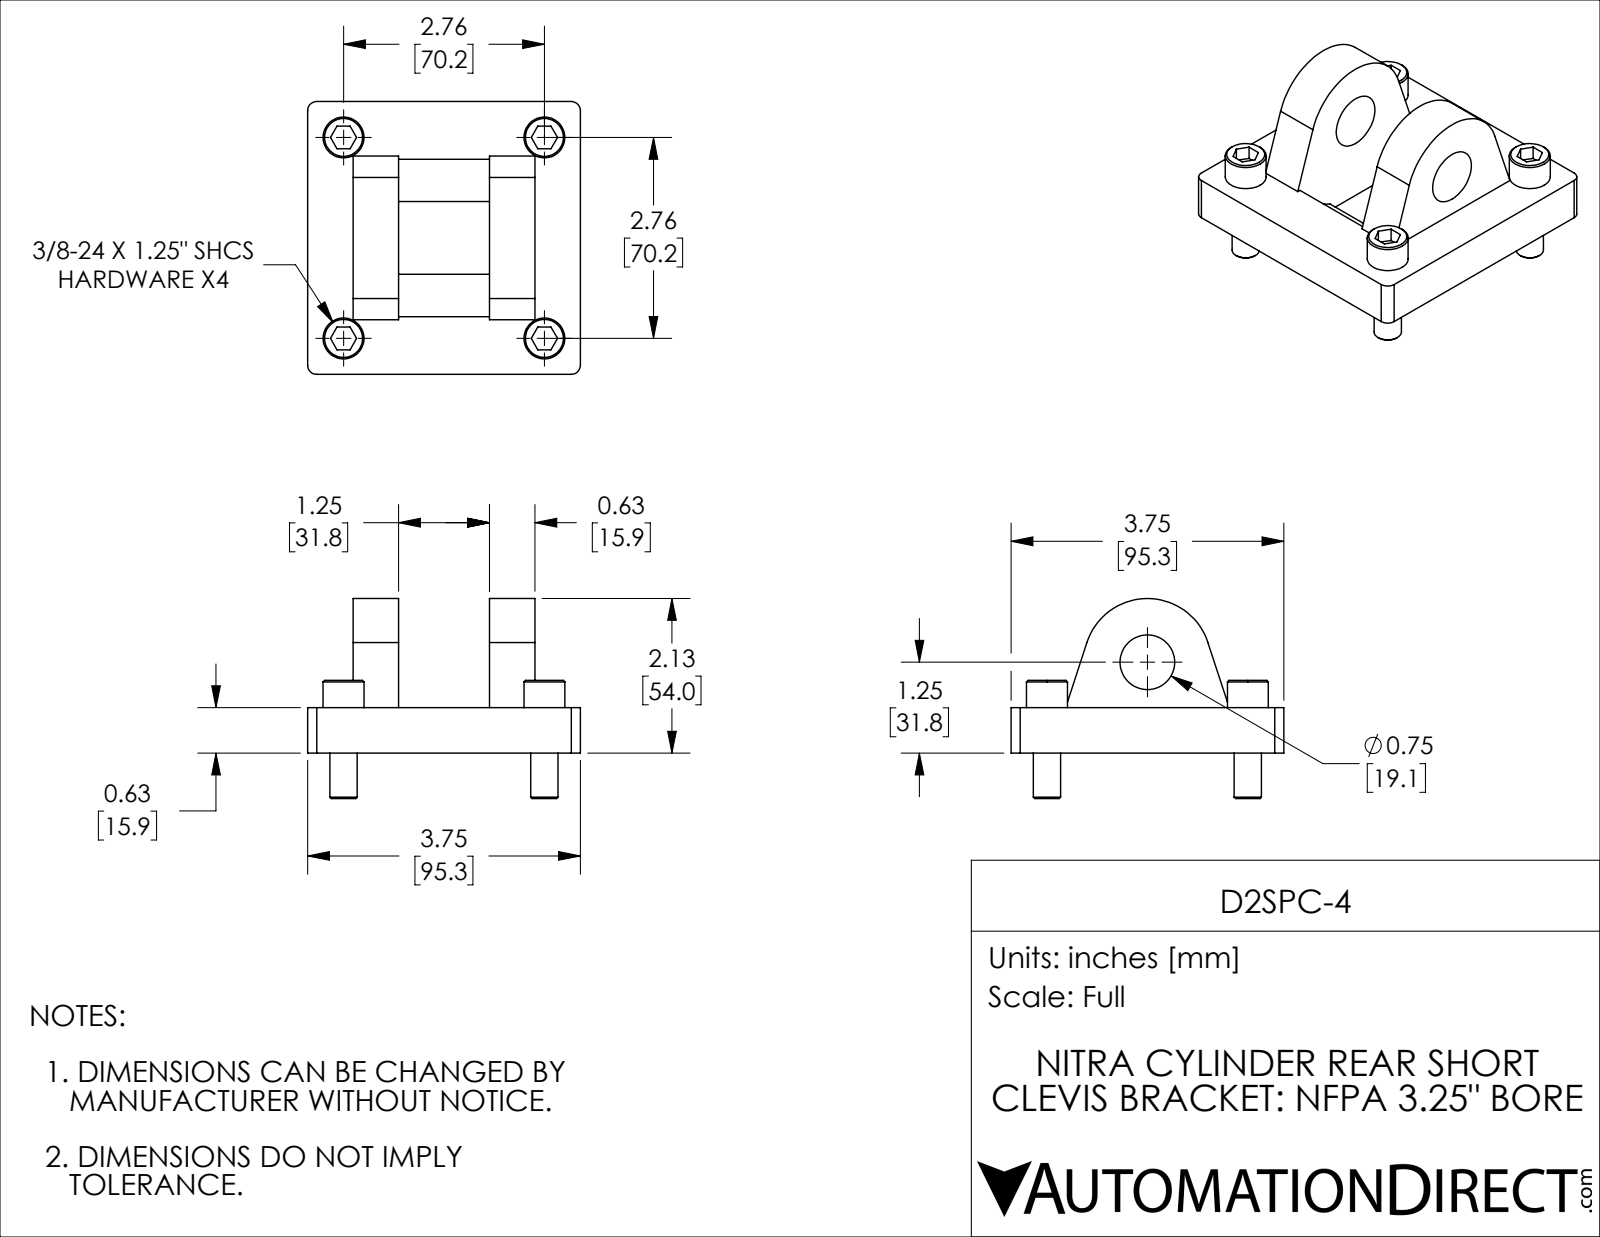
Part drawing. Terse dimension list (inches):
name: D2SPC-4
written by: SolidWorks 2019 (CONFIG_CONTROL_DESIGN)
unit: in
bodies: 5 solids, 119 faces (62 planar, 41 cylindrical, 16 other)
size: 3.75 × 3.75 × 2.75
volume: 10.63 in³; area: 64.42 in²
holes: 4× ⌀0.406, 1× ⌀0.752
bosses: 4× ⌀0.562, 2× ⌀0.375, 2× ⌀0.375
rounds: 4× R0.125, 1× R0.875, 1× R1.25
face distances: 0.625, 0.625, 2.5, 1.875, 1.25, 1.25, 3.75, 2.5, 1.25, 3.75
hole spacings: 2.762, 3.906
